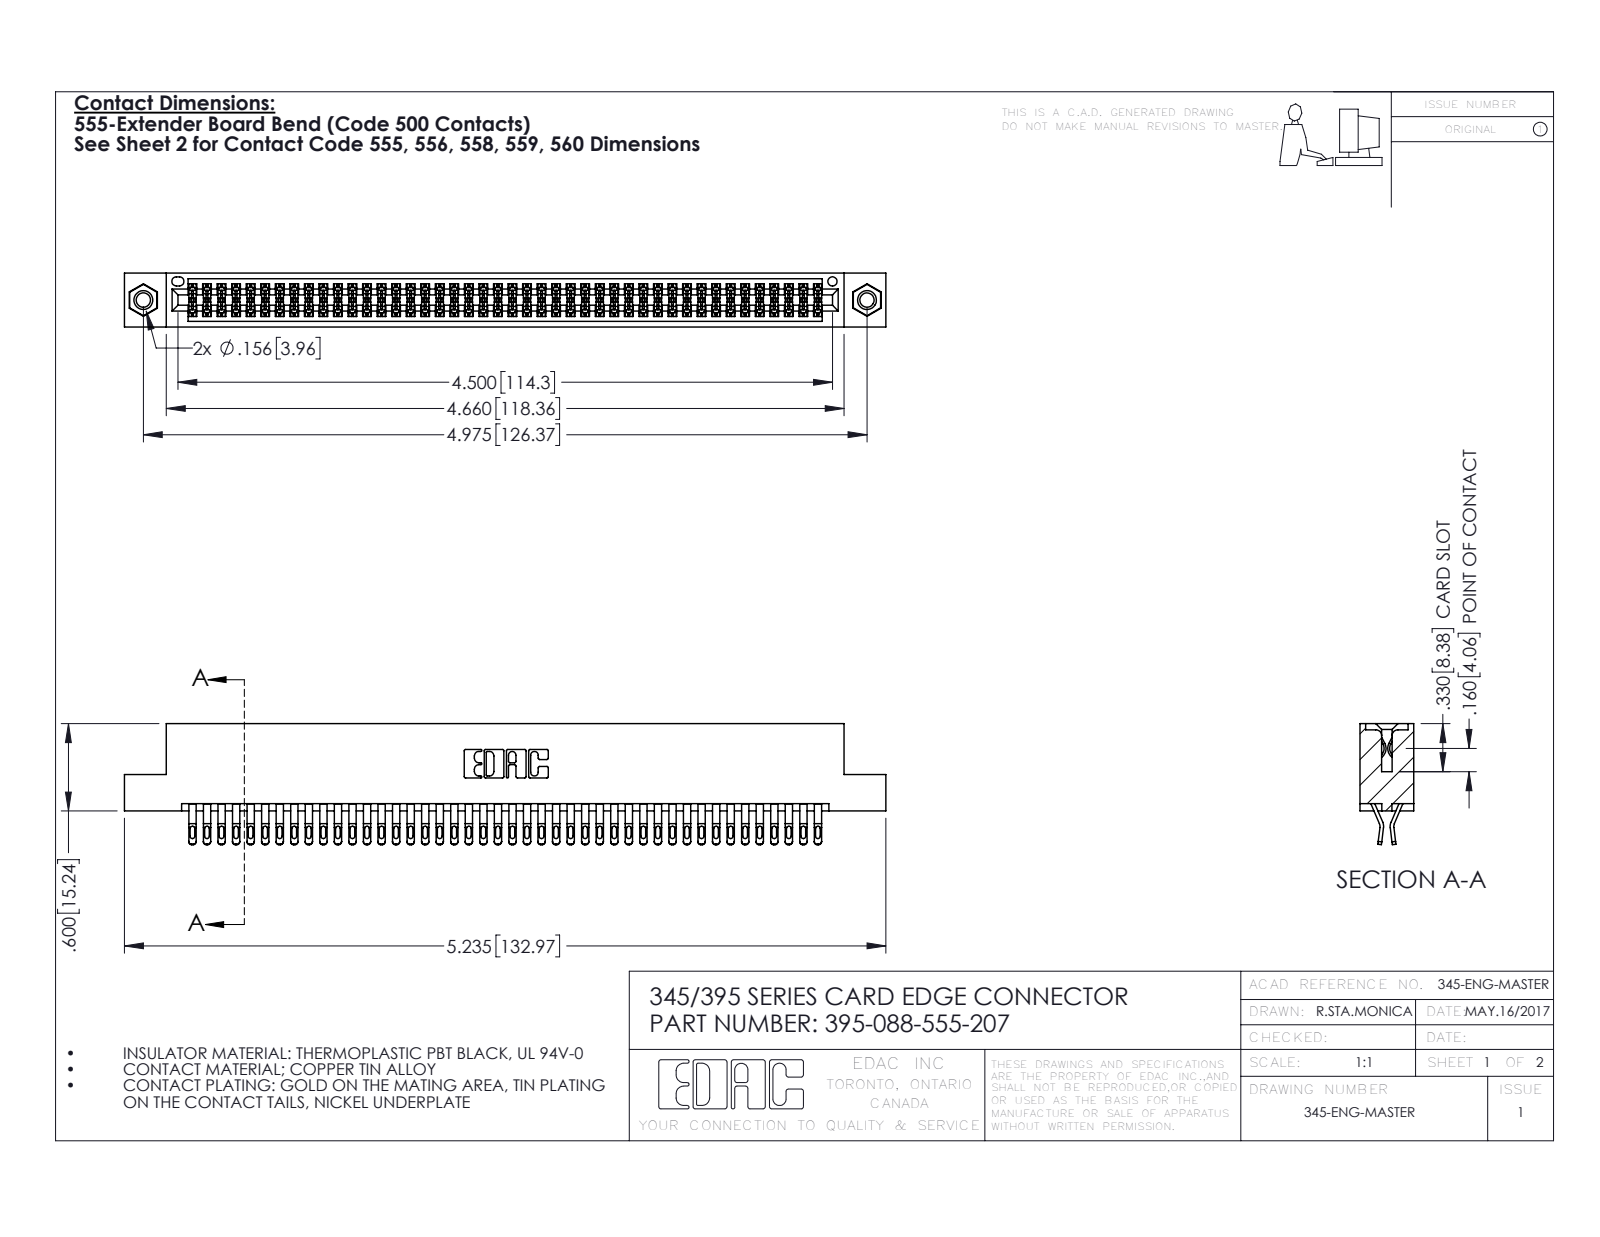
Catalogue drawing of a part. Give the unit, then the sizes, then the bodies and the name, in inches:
Units: inches
Overall size (bounding box): 5.235 × 0.832 × 0.37
Round holes (diameter × count): ⌀0.098 ×2, ⌀0.125 ×2, ⌀0.156 ×2, ⌀0.064 ×1
Round bosses / shafts (diameter × count): ⌀0.155 ×2
Partial cylindrical surfaces — rounded edges, fillets, slot ends (radius × count): R0.016 ×220, R0.02 ×176, R0.006 ×132, R0.01 ×22, R0.007 ×6, R0.031 ×6, R0.026 ×3, R0.01 ×2
Main face-to-face distances: 0.072, 0.298, 0.025, 0.37, 0.2, 0.098, 0.272, 0.225, 0.175, 0.149
Hole centre spacings: 0.27, 4.739, 4.975
Volume: 0.804 in³ · Surface area: 31.67 in²
Bodies: 91 solids, 5114 faces (2840 planar, 2258 cylindrical, 16 other)
Part name (STEP PRODUCT): 345-250-001_345-250-005-103; 395-088-555-207; 345 Part_Flush Mounting Lugs - 0.156 Dia-TI; 345-292-001_555 Tail
STEP written by: SolidWorks 2016 (CONFIG_CONTROL_DESIGN)
